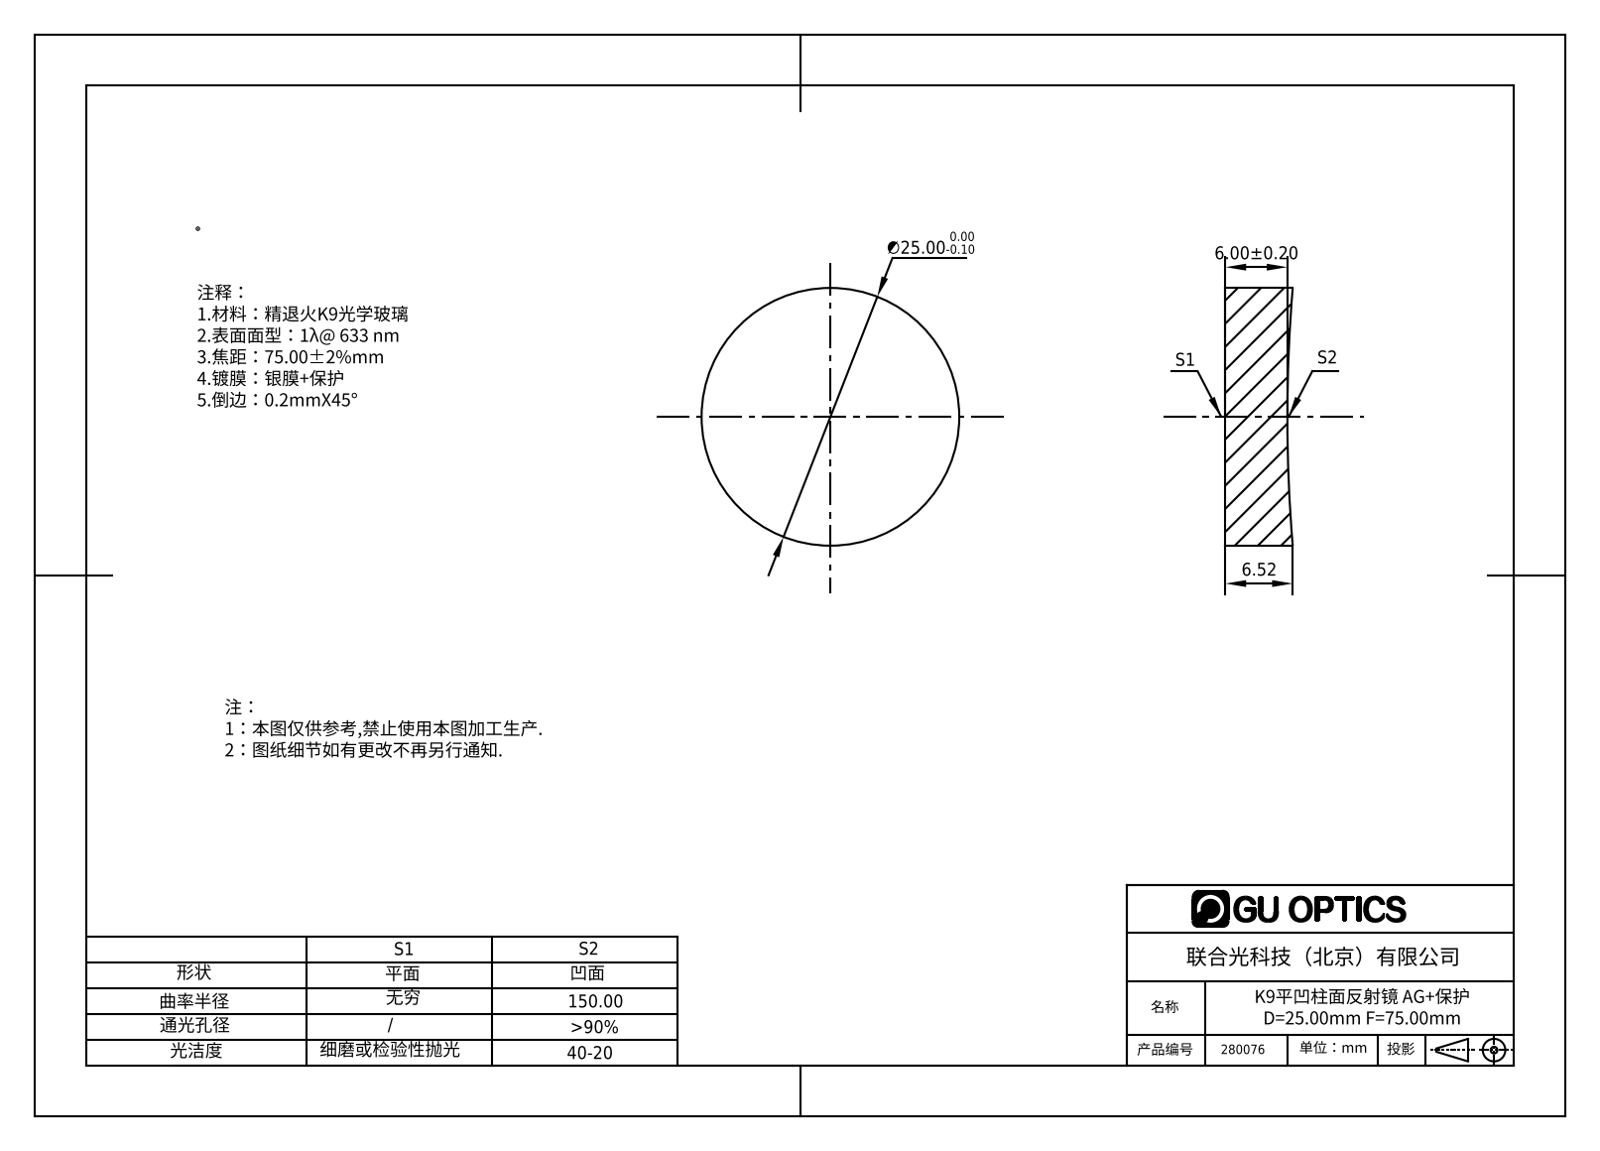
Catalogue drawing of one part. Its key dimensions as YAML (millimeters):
part_name: "280010"
step_written_by: "SolidWorks 2020 (CONFIG_CONTROL_DESIGN)"
units: millimeters
bodies: {solids: 1, faces: 3, planar: 1, cylindrical: 2, other: 0}
overall_size: [25, 25, 6.52]
volume: 3009
surface_area: 1474
round_bosses_or_shafts:
  - {diameter: 25, count: 1}
partial_cylinders:
  - {radius: 150, count: 1}
